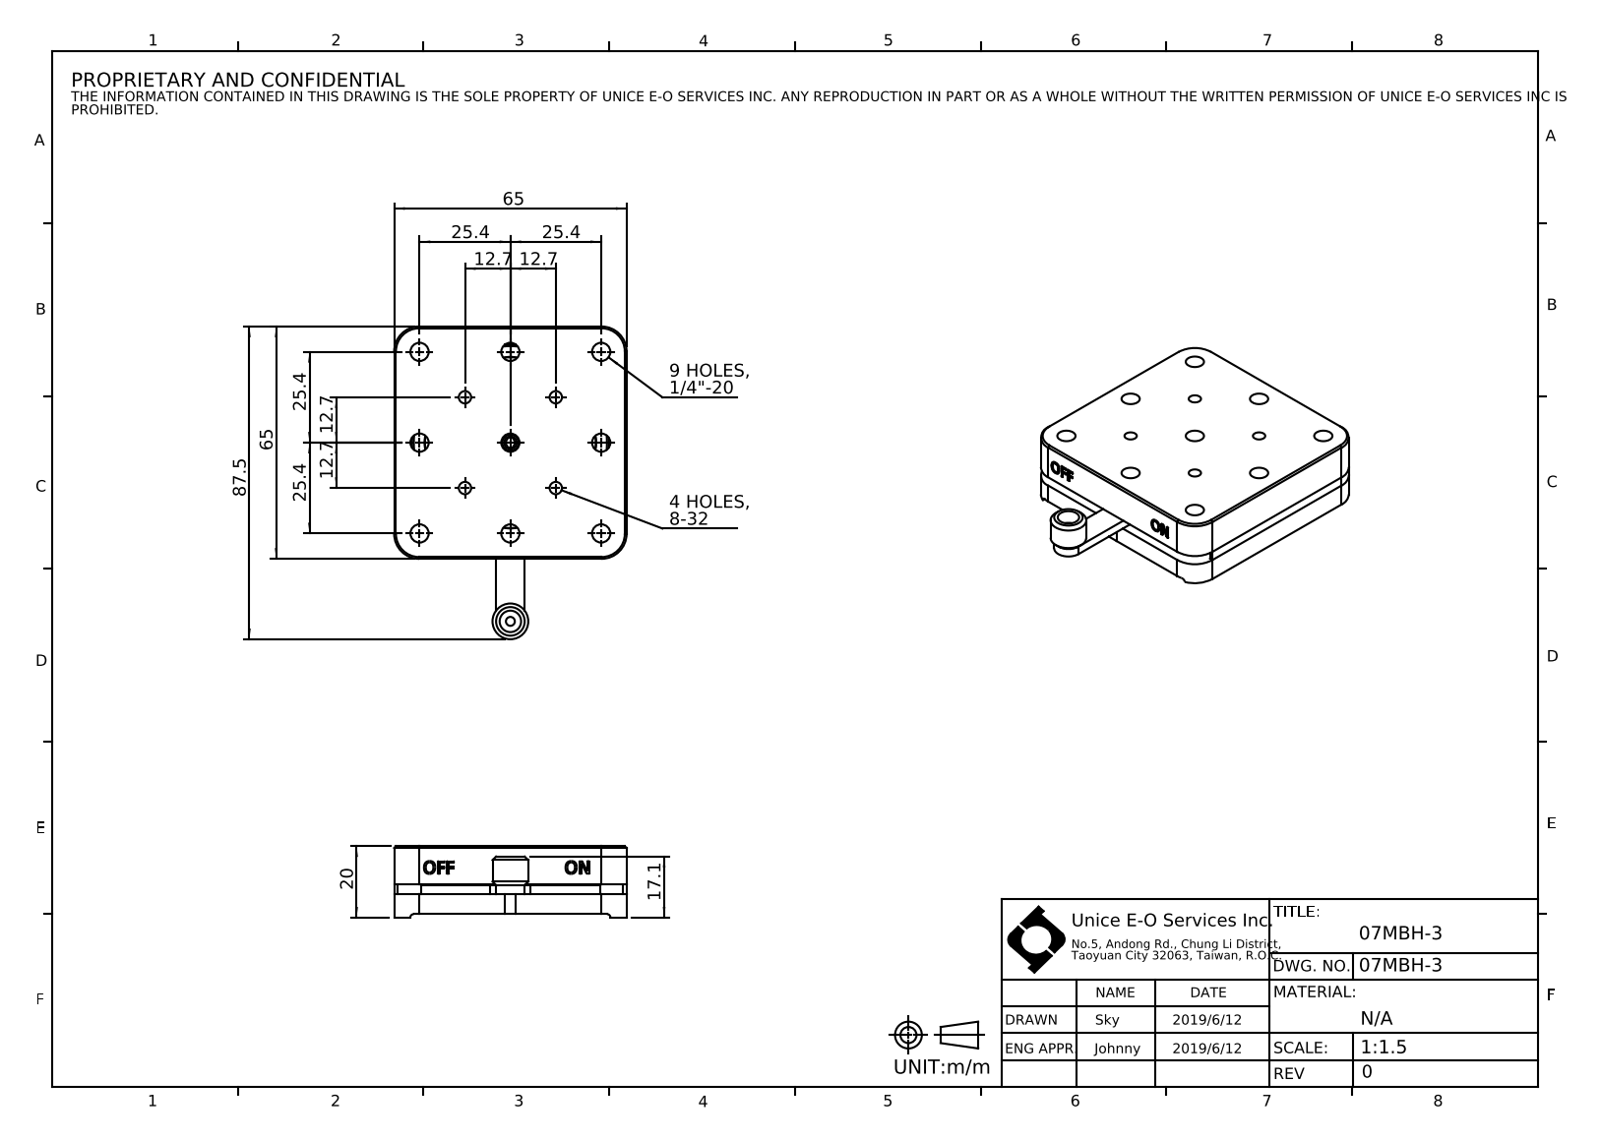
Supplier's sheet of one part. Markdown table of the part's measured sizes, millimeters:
| quantity | value |
| --- | --- |
| part name | 07MBH-3 |
| STEP written by | SolidWorks 2016 (CONFIG_CONTROL_DESIGN) |
| units | millimeters |
| bodies | 0 solids, 173 faces (90 planar, 61 cylindrical, 22 other) |
| overall size | 87.5 × 65 × 20 |
| round holes (diameter × count) | 5.11 × 9, 6 × 7, 3.45 × 4, 2.5 × 1 |
| round bosses / shafts (diameter × count) | 10 × 1 |
| partial cylindrical surfaces (radius × count) | 7 × 4, 1 × 2, 4 × 1 |
| main face-to-face distances | 2.8, 13.5, 10.7, 5.5, 8.3, 19, 65, 8.1, 2.6, 10.9 |
| hole center spacings | 17.96, 25.4, 40.16, 35.92, 56.8, 50.8, 9.27, 15.76 |
